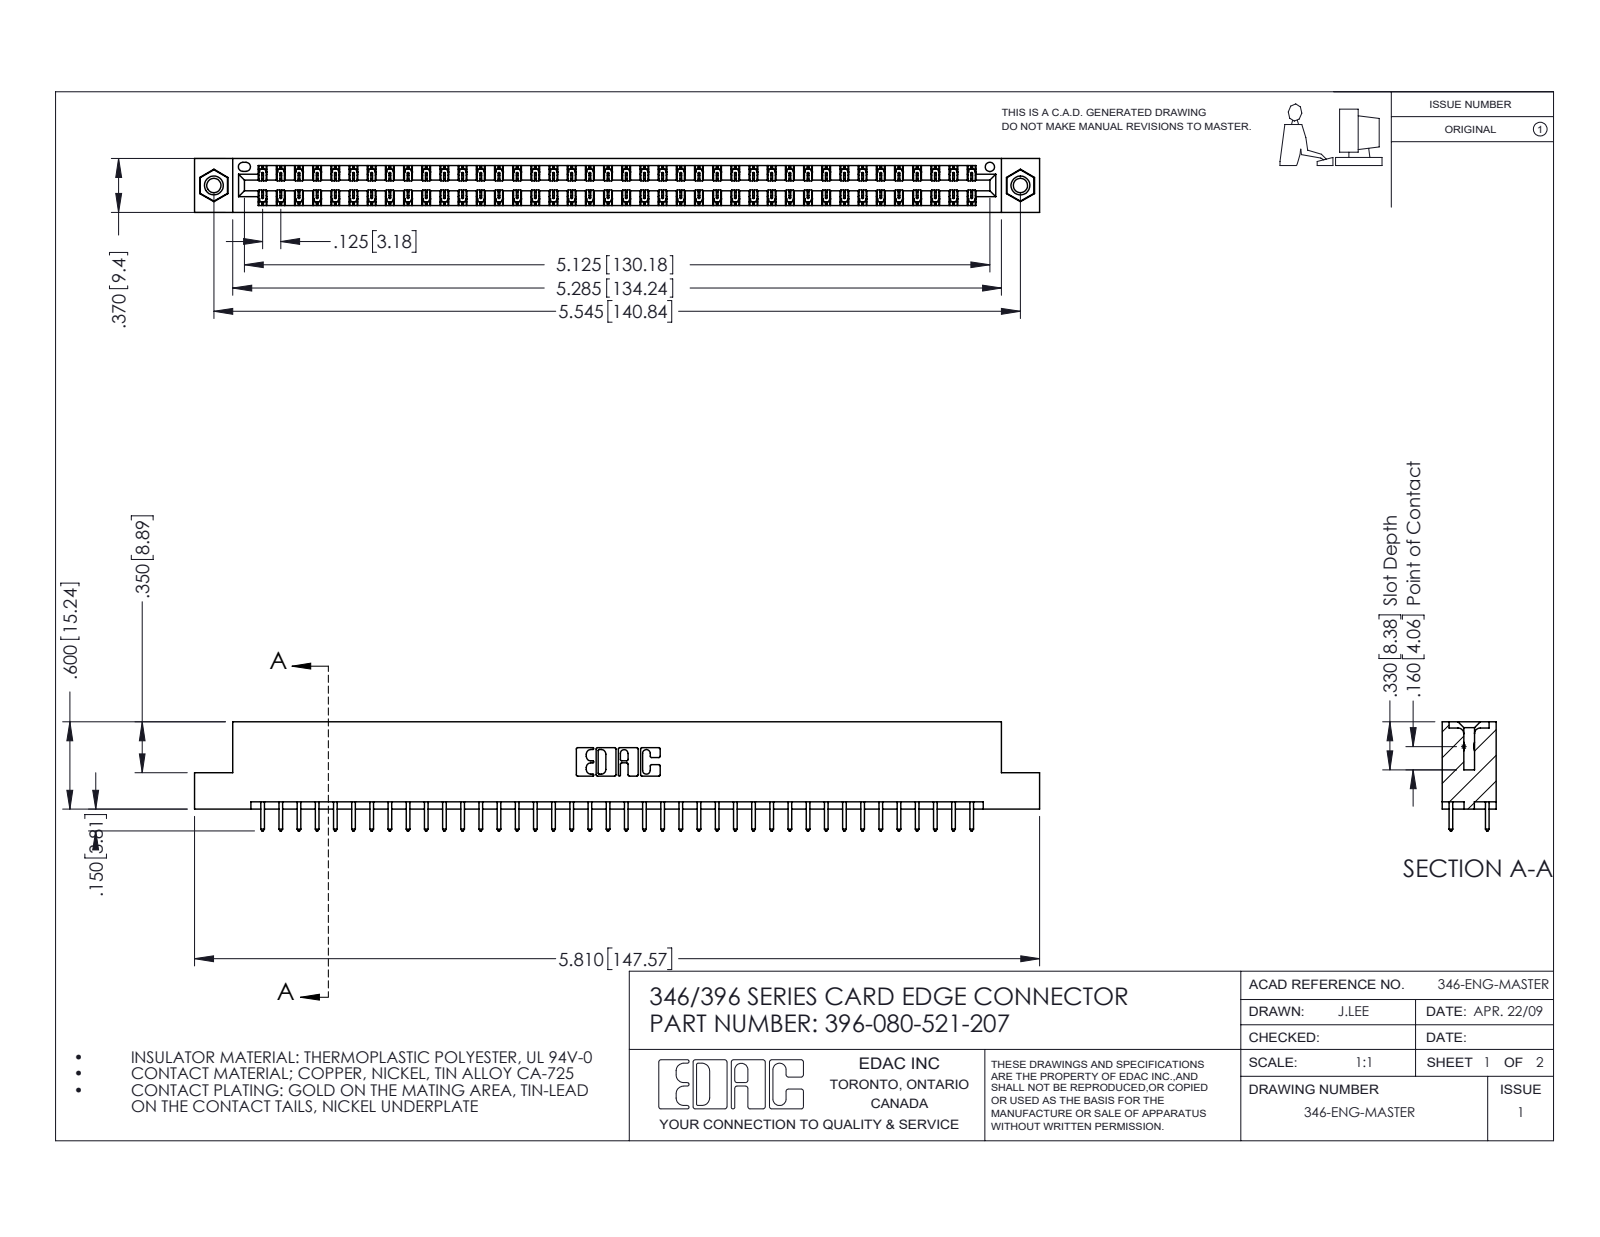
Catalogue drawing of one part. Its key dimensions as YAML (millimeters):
part_name: "346 Part_Flush Mounting Lugs - 0.156 Dia-TI; 396-080-521-207; 345-292-001_345-293-121; 345-250-001_345-250-005-103"
step_written_by: "SolidWorks 2016 (CONFIG_CONTROL_DESIGN)"
units: millimeters
bodies: {solids: 83, faces: 4342, planar: 2908, cylindrical: 1418, other: 16}
overall_size: [147.6, 19.1, 9.4]
volume: 14300
surface_area: 19480
round_holes:
  - {diameter: 2.5, count: 2}
  - {diameter: 3.2, count: 2}
  - {diameter: 4, count: 2}
  - {diameter: 1.6, count: 1}
round_bosses_or_shafts:
  - {diameter: 3.9, count: 2}
partial_cylinders:
  - {radius: 0.2, count: 120}
  - {radius: 0.3, count: 80}
  - {radius: 0.3, count: 22}
  - {radius: 0.2, count: 6}
  - {radius: 0.8, count: 6}
  - {radius: 0.7, count: 3}
  - {radius: 0.4, count: 2}
  - {radius: 0.6, count: 2}
face_to_face_distances: [1.2, 8.2, 6.4, 9.4, 1.8, 7.6, 0.6, 7, 3.8, 5.6]
hole_center_spacings: [6.2, 135.5, 140.8]
